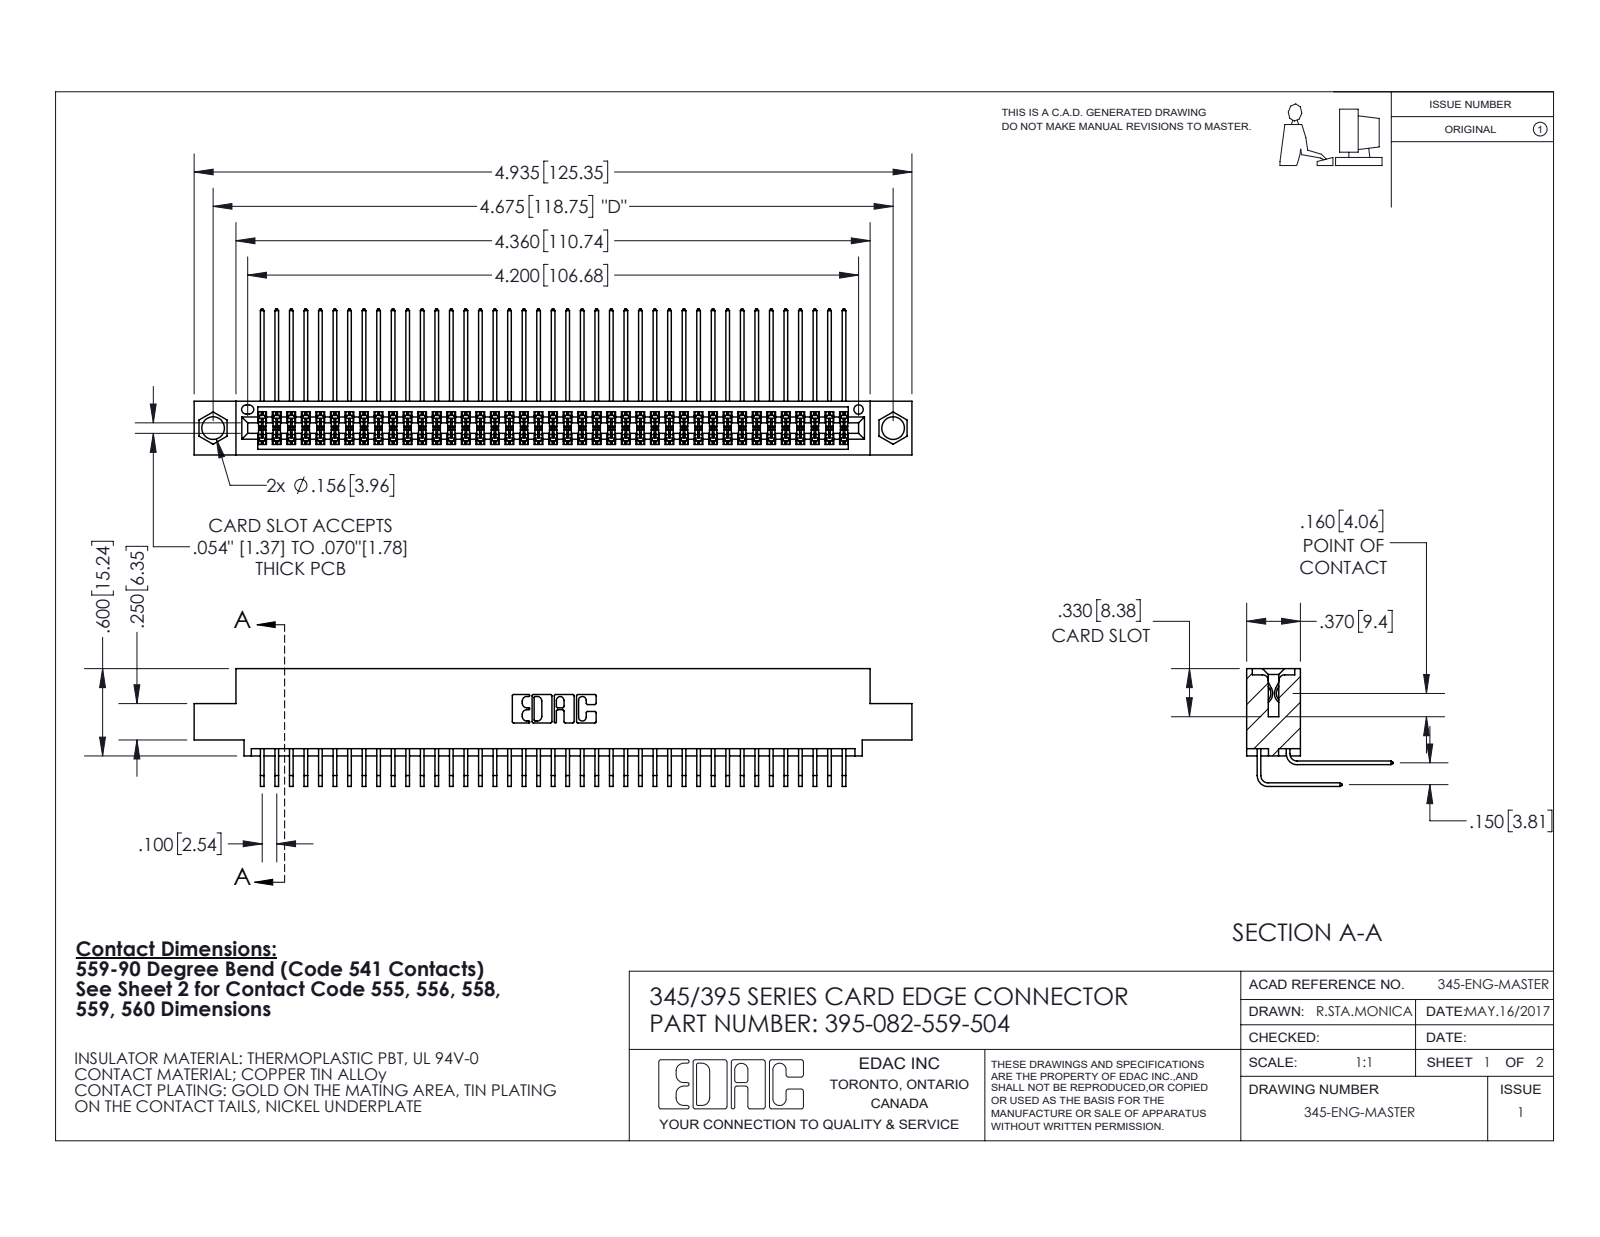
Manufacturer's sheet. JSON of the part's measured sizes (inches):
{"part_name": "395-082-559-504; 345 Part_0.110 Offset - 0.156 Dia-TI; 345-292-001_558 559 Tail - 1; 345-292-001_559 Tail - 2", "step_written_by": "SolidWorks 2020 (CONFIG_CONTROL_DESIGN)", "units": "inches", "bodies": {"solids": 83, "faces": 4408, "planar": 2968, "cylindrical": 1440, "other": 0}, "overall_size": [4.935, 1.005, 0.809], "volume_in3": 0.76, "surface_area_in2": 31.88, "round_holes": [[0.156, 2], [0.064, 1]], "partial_cylinders_radius": [[0.006, 123], [0.01, 22], [0.007, 6], [0.031, 6], [0.026, 3], [0.014, 2], [0.019, 2], [0.022, 2]], "face_to_face_distances": [0.072, 0.298, 0.37, 0.2, 0.098, 0.272, 0.025, 0.225, 0.175, 0.15], "hole_center_spacings": [0.27, 4.439, 4.675]}
